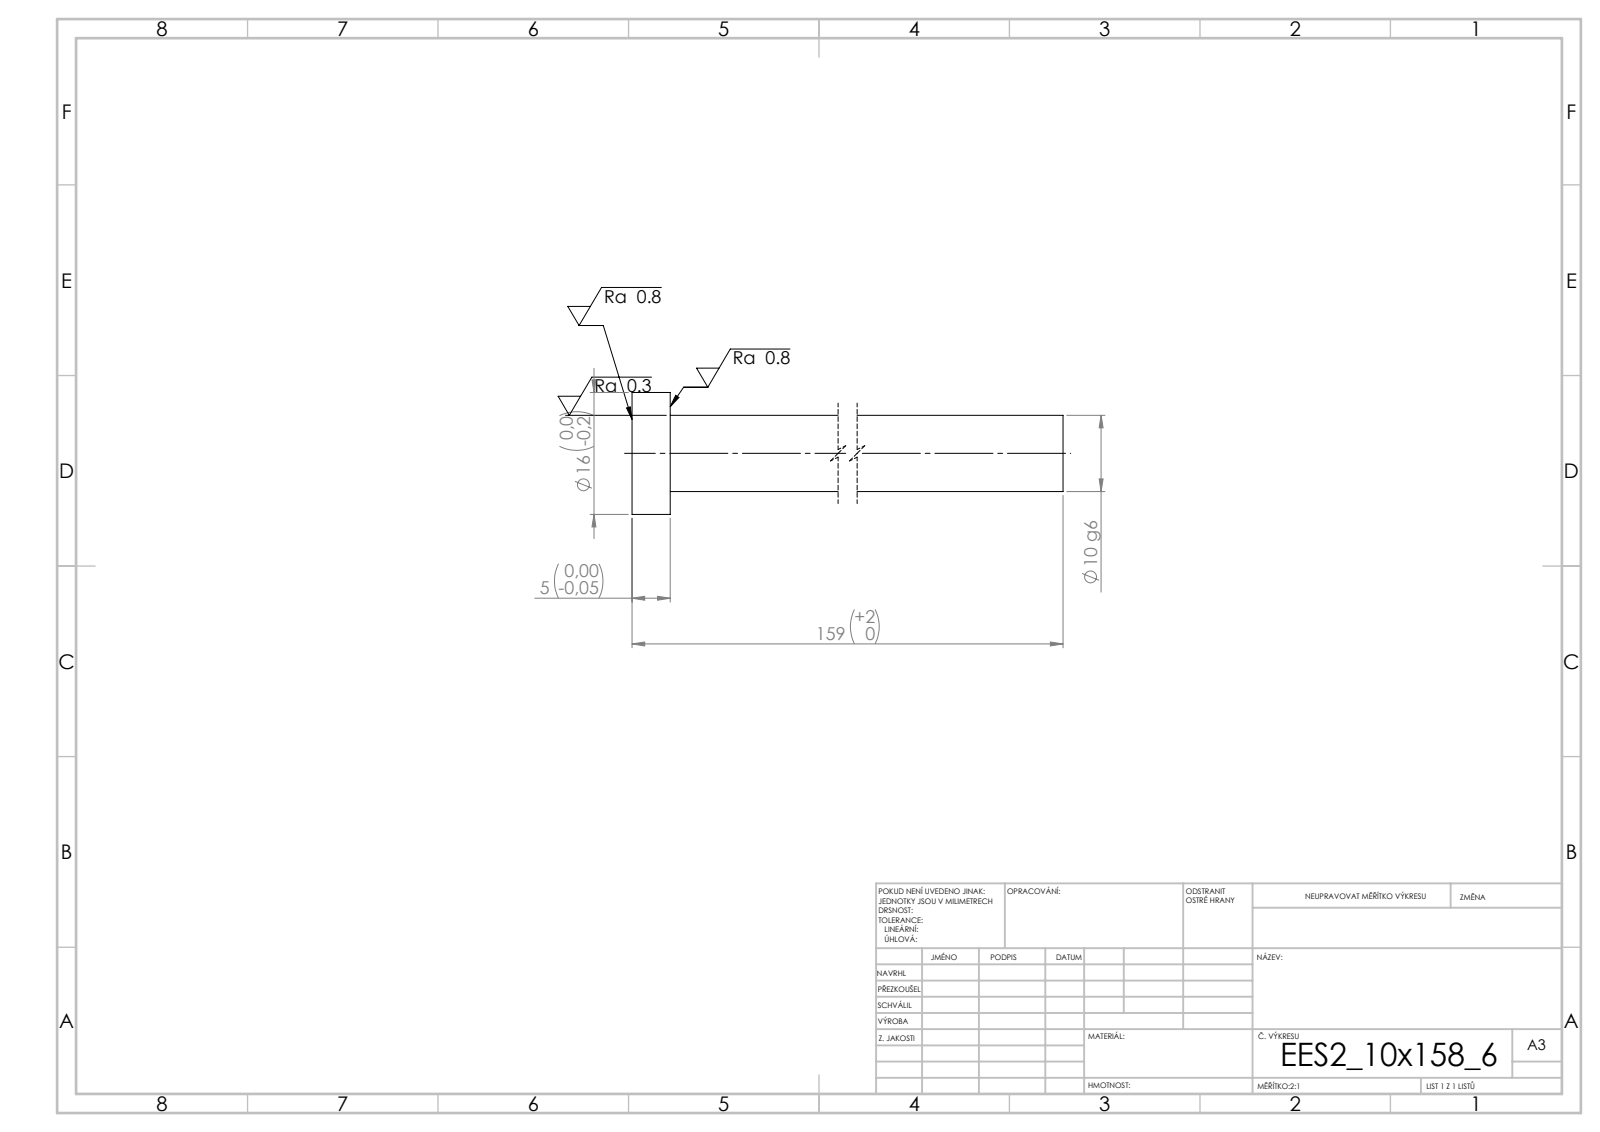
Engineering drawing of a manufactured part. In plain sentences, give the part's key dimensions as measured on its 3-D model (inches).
Its 3-D file was written by "SolidWorks 2019 (CONFIG_CONTROL_DESIGN)". It is 1 solid with 7 faces: 3 planar, 4 cylindrical and 0 other. Overall it measures 6.244 by 0.63 by 0.63 inches. Its volume is 0.798 cubic inches and its surface area 8.492 square inches. Round bosses or shafts: 1 of diameter 0.63, 1 of diameter 0.394. The main face-to-face distances are 0.197, 6.244, 6.047.
